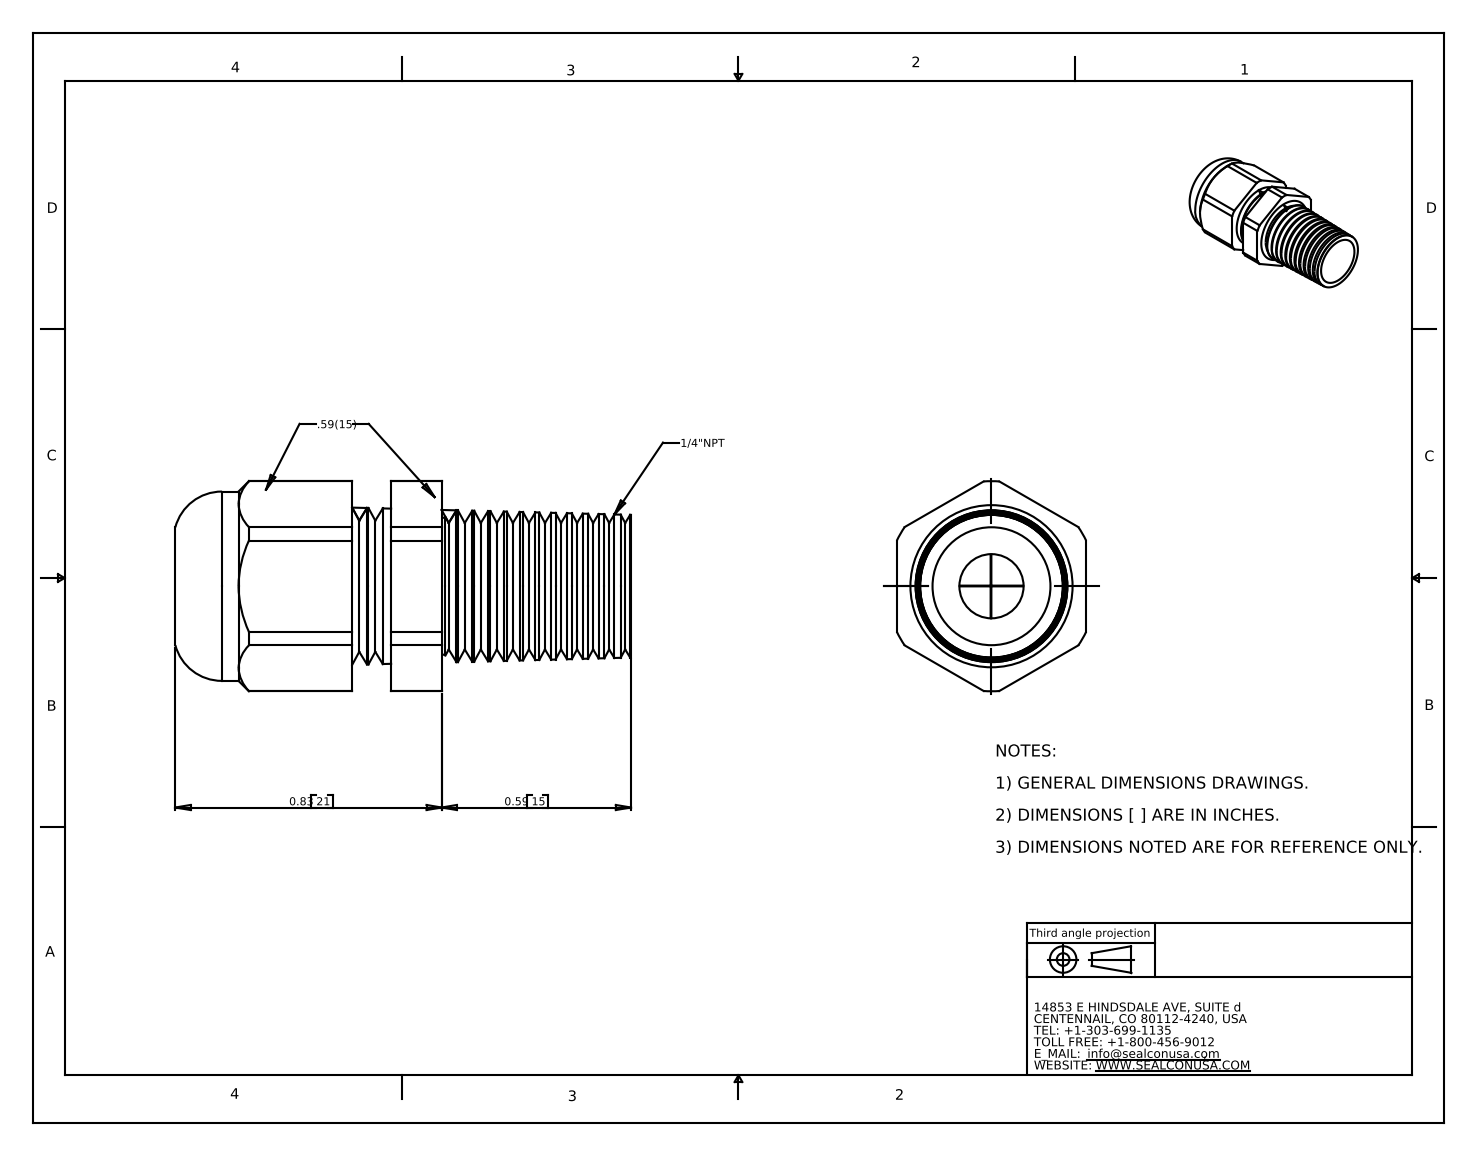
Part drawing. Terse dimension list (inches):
name: CD07CR-GY
written by: SolidWorks 2007 (CONFIG_CONTROL_DESIGN)
unit: in
bodies: 2 solids, 141 faces (19 planar, 22 cylindrical, 100 other)
size: 1.42 × 0.655 × 0.59
volume: 0.23 in³; area: 5.352 in²
holes: 1× ⌀0.2, 1× ⌀0.367
bosses: 1× ⌀0.59
rounds: 1× R0.327
face distances: 0.59, 0.476, 0.354, 0.122, 0.633, 0.279, 0.157, 0.167, 0.521, 0.643
